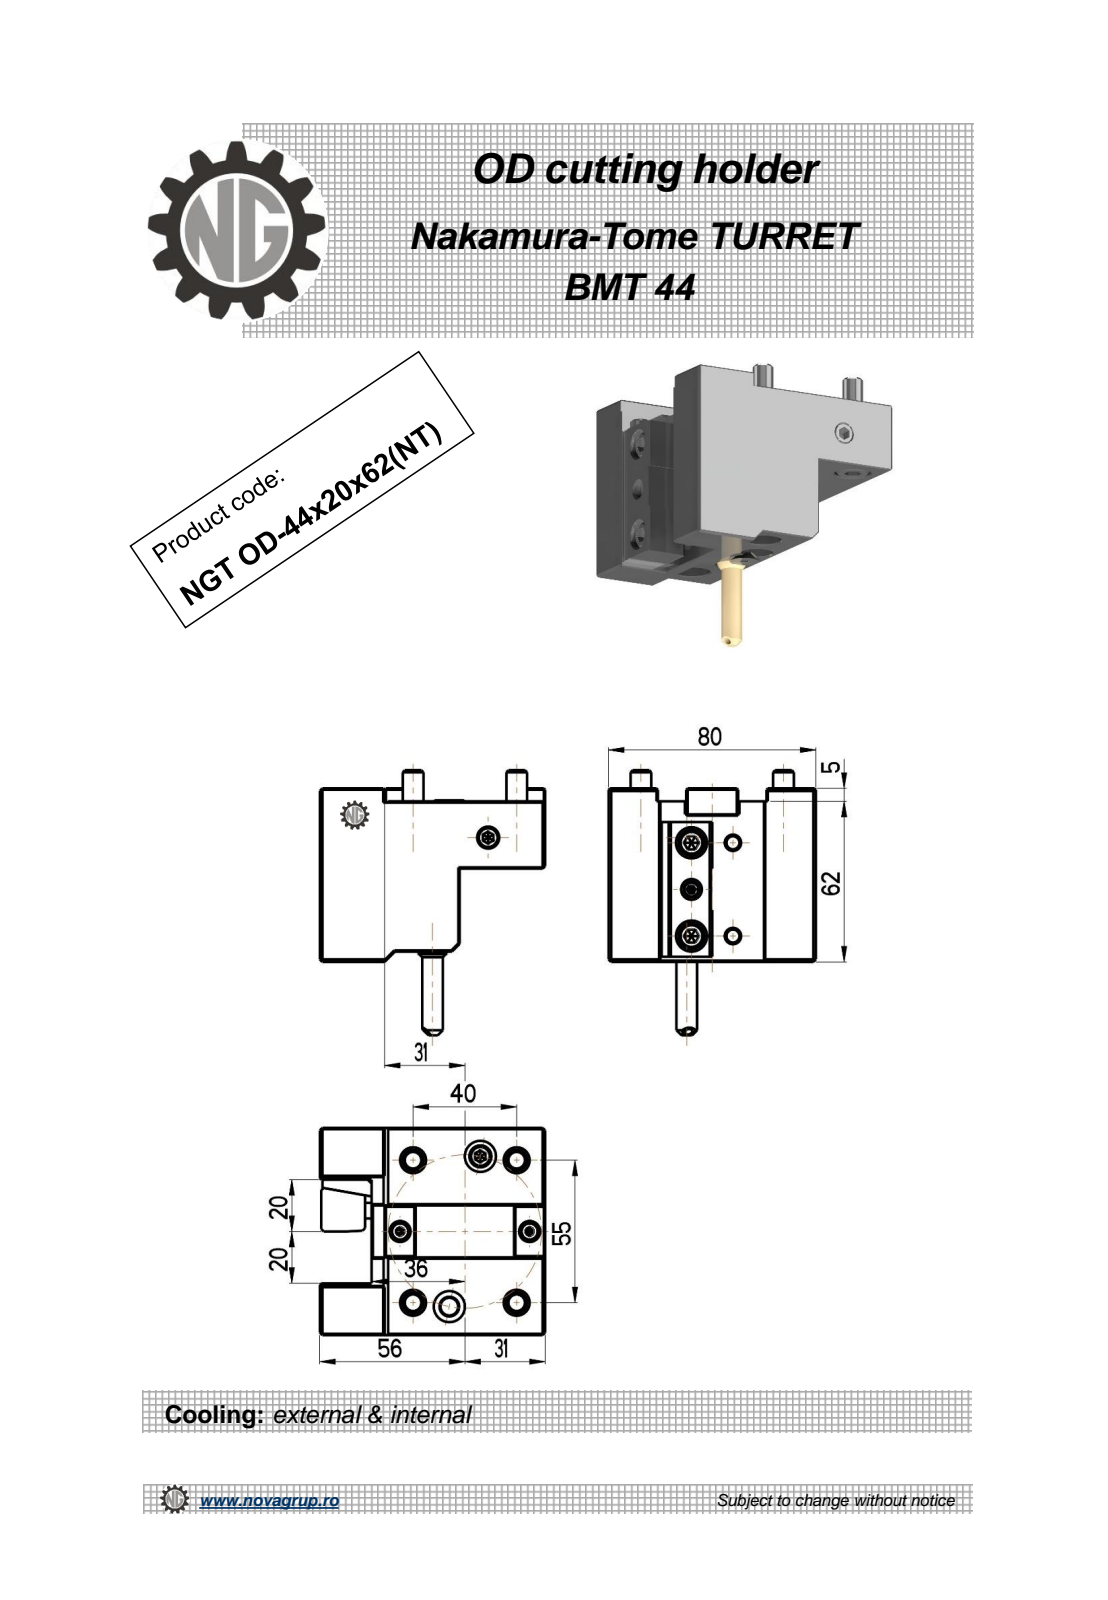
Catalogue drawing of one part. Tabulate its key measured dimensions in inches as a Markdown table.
| quantity | value |
| --- | --- |
| part name | NGT_OD_44_20_62_NT |
| STEP written by | PRO/ENGINEER BY PARAMETRIC TECHNOLOGY CORPORATION, 2010280 (CONFIG_CONTROL_DESIGN) |
| units | inches |
| bodies | 1 solid, 210 faces (134 planar, 43 cylindrical, 33 other) |
| overall size | 4.029 × 3.425 × 3.15 |
| volume | 18.38 in³ |
| surface area | 61.82 in² |
| round holes (diameter × count) | 0.472 × 2, 0.118 × 1, 0.197 × 1, 0.268 × 1 |
| round bosses / shafts (diameter × count) | 0.315 × 5, 0.236 × 3, 0.441 × 1 |
| partial cylindrical surfaces (radius × count) | 0.009 × 6, 0.016 × 6, 0.039 × 1 |
| main face-to-face distances | 0.787, 3.15, 2.638, 2.126, 1.024, 0.197, 1.339, 0.394, 1.299, 2.362 |
| hole center spacings | 1.05, 1.549, 2.332 |
